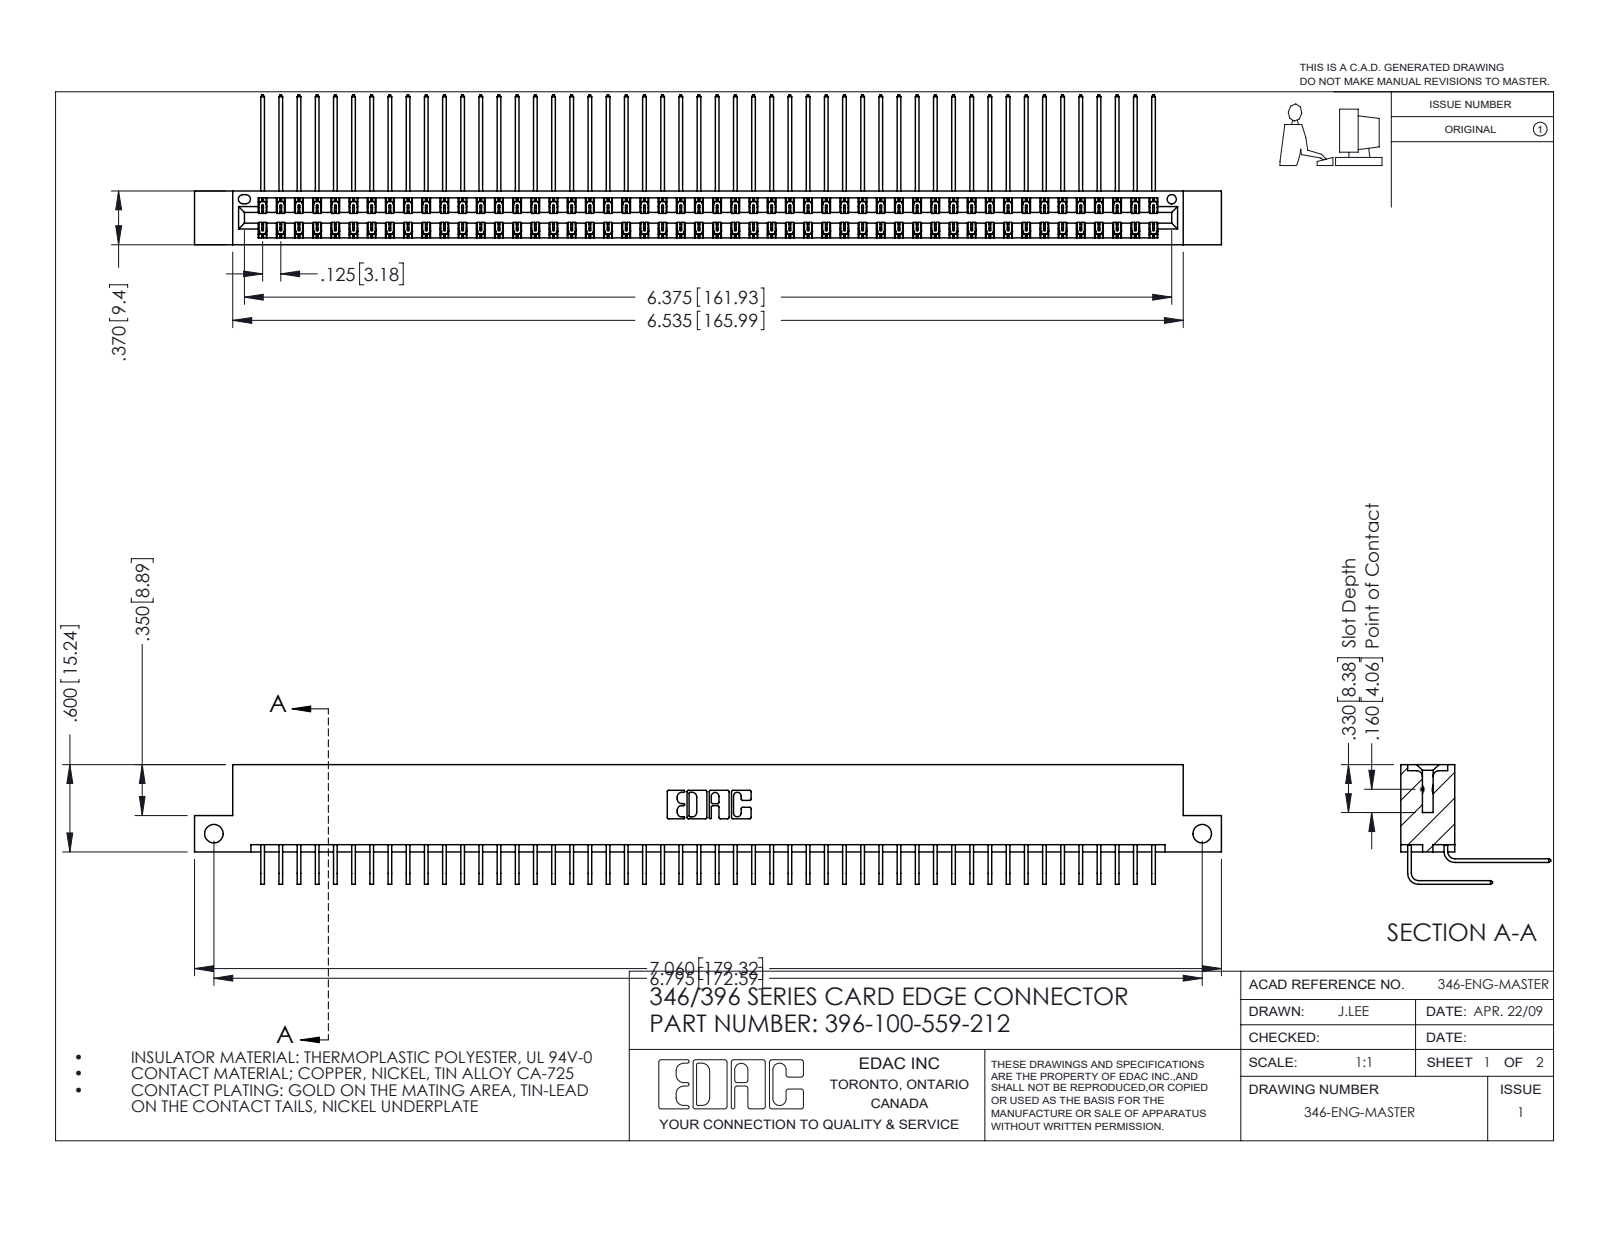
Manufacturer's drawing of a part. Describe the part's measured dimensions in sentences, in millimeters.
The part is named "346 Part_Flush Mounting Lugs - Side Mount; 345-292-001_558 559 Tail - 1; 396-100-559-212; 345-292-001_559 Tail - 2". Its 3-D file was written by "SolidWorks 2016 (CONFIG_CONTROL_DESIGN)". It is 101 solids with 5522 faces: 3776 planar, 1746 cylindrical and 0 other. Overall it measures 179.3 by 26.2 by 20.9 millimeters. Its volume is 18 040 cubic millimeters and its surface area 27 550 square millimeters. Round holes: 2 of diameter 3.3, 1 of diameter 1.6. Partial cylindrical surfaces (rounded edges, fillets, slot ends): 150 of radius 0.2, 22 of radius 0.3, 6 of radius 0.2, 6 of radius 0.8, 3 of radius 0.7, 2 of radius 0.4, 2 of radius 0.6, 2 of radius 0.6. The main face-to-face distances are 1.2, 8.2, 0.6, 9.4, 6.4, 1.8, 7.6, 7, 3.8, 5.6. The hole center spacings are 172.6.
